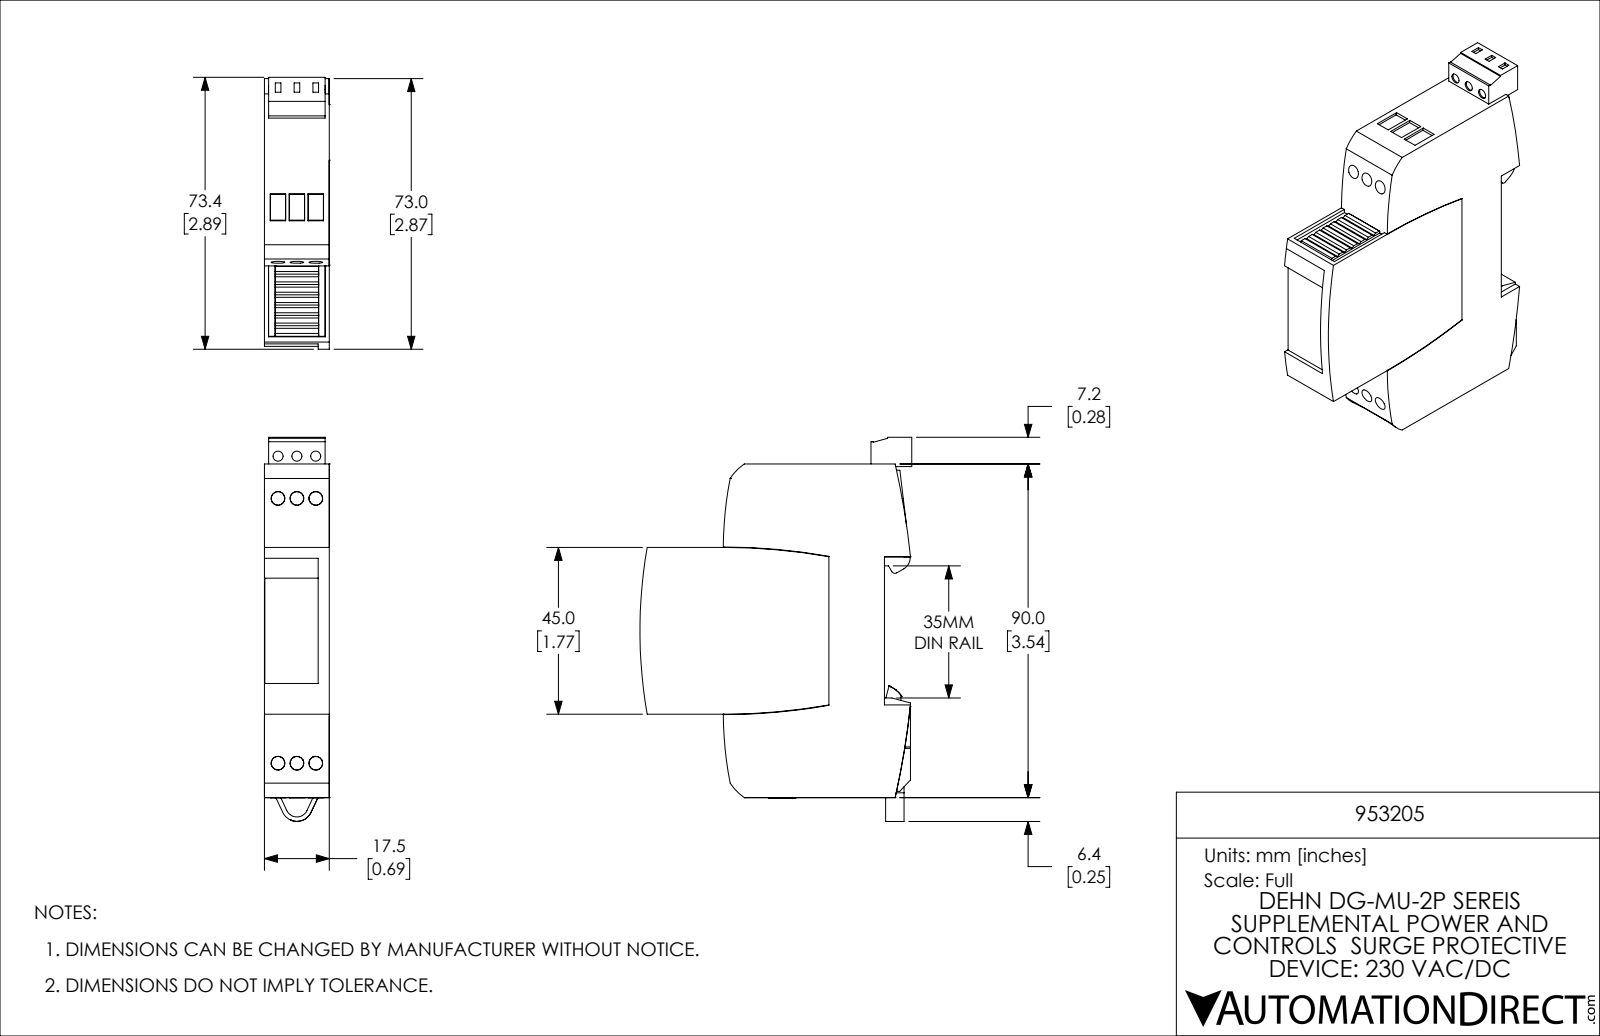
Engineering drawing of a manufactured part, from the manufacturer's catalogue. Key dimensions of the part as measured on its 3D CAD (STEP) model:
Part name (STEP PRODUCT): 953205
STEP written by: SolidWorks 2019 (CONFIG_CONTROL_DESIGN)
Units: inches
Bodies: 1 solid, 255 faces (198 planar, 38 cylindrical, 19 other)
Overall size (bounding box): 4.079 × 2.888 × 0.689
Volume: 5.435 in³ · Surface area: 27.21 in²
Round holes (diameter × count): ⌀0.106 ×3
Partial cylindrical surfaces — rounded edges, fillets, slot ends (radius × count): R6.448 ×2, R6.449 ×2, R0.039 ×1, R0.098 ×1, R0.118 ×1, R0.138 ×1, R3.937 ×1, R3.94 ×1
Main face-to-face distances: 0.689, 0.685, 3.543, 0.016, 0.673, 2.518, 0.276, 2.794, 0.898, 2.646
Hole centre spacings: 0.2, 0.4
